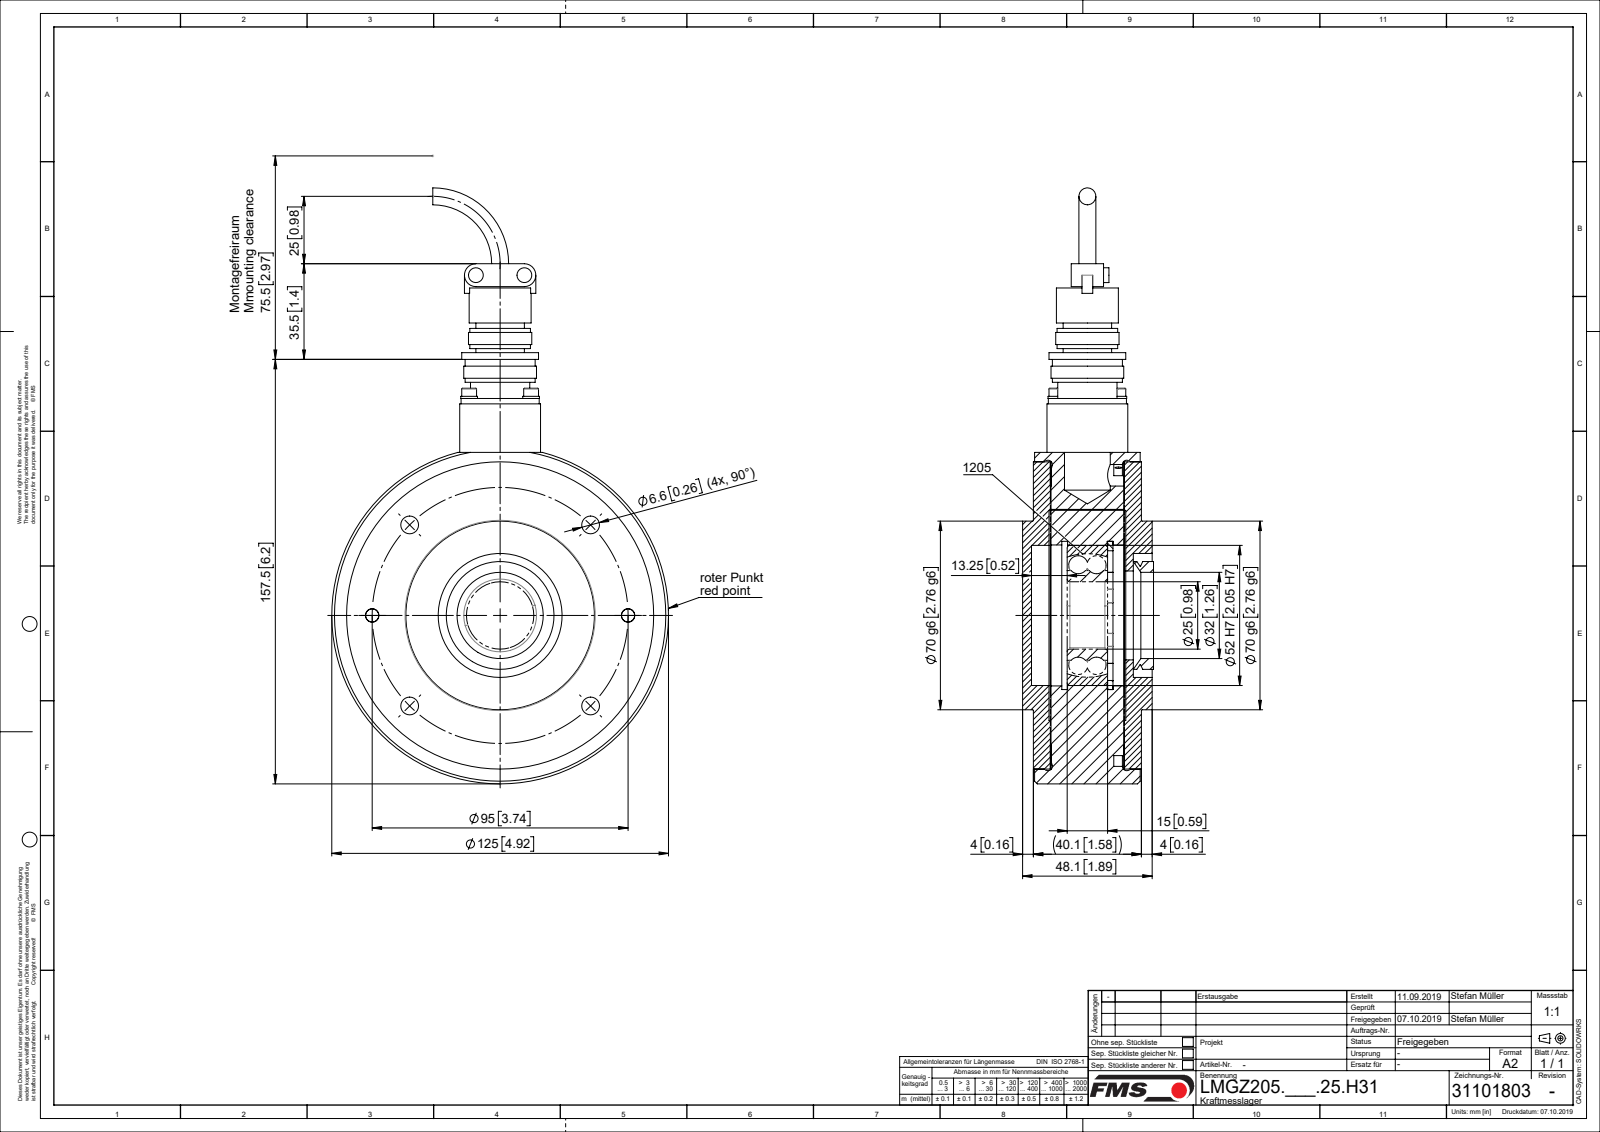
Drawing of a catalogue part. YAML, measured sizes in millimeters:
part_name: "ZEICHNUNG1; L49693; L4832404; L47956 (+8 more)"
step_written_by: "Mechanical Desktop 2007 (CONFIG_CONTROL_DESIGN)"
units: millimeters
bodies: {solids: 20, faces: 406, planar: 110, cylindrical: 244, other: 52}
overall_size: [221.15, 125, 48.1]
volume: 481544
surface_area: 144443
round_holes:
  - {diameter: 6.6, count: 6}
  - {diameter: 2.6, count: 4}
  - {diameter: 3.2, count: 4}
  - {diameter: 3.4, count: 4}
  - {diameter: 5, count: 2}
  - {diameter: 11, count: 2}
  - {diameter: 23, count: 1}
  - {diameter: 25, count: 1}
  - {diameter: 31, count: 1}
  - {diameter: 33, count: 1}
  - {diameter: 37.9, count: 1}
  - {diameter: 46, count: 1}
round_bosses_or_shafts:
  - {diameter: 5.5, count: 6}
  - {diameter: 6.2, count: 4}
  - {diameter: 3, count: 4}
  - {diameter: 2.5, count: 4}
  - {diameter: 10, count: 2}
  - {diameter: 6, count: 2}
  - {diameter: 125, count: 1}
  - {diameter: 114, count: 1}
partial_cylinders:
  - {radius: 5, count: 8}
  - {radius: 4.25, count: 2}
  - {radius: 40.5, count: 1}
  - {radius: 47, count: 1}
face_to_face_distances: [27.25, 33.55, 6.3, 6.55, 33.8, 27, 27.5, 4, 10.55, 37.8]
hole_center_spacings: [47.5, 16.26, 23, 36.36, 67.18, 87.77, 32.53, 95.01]
